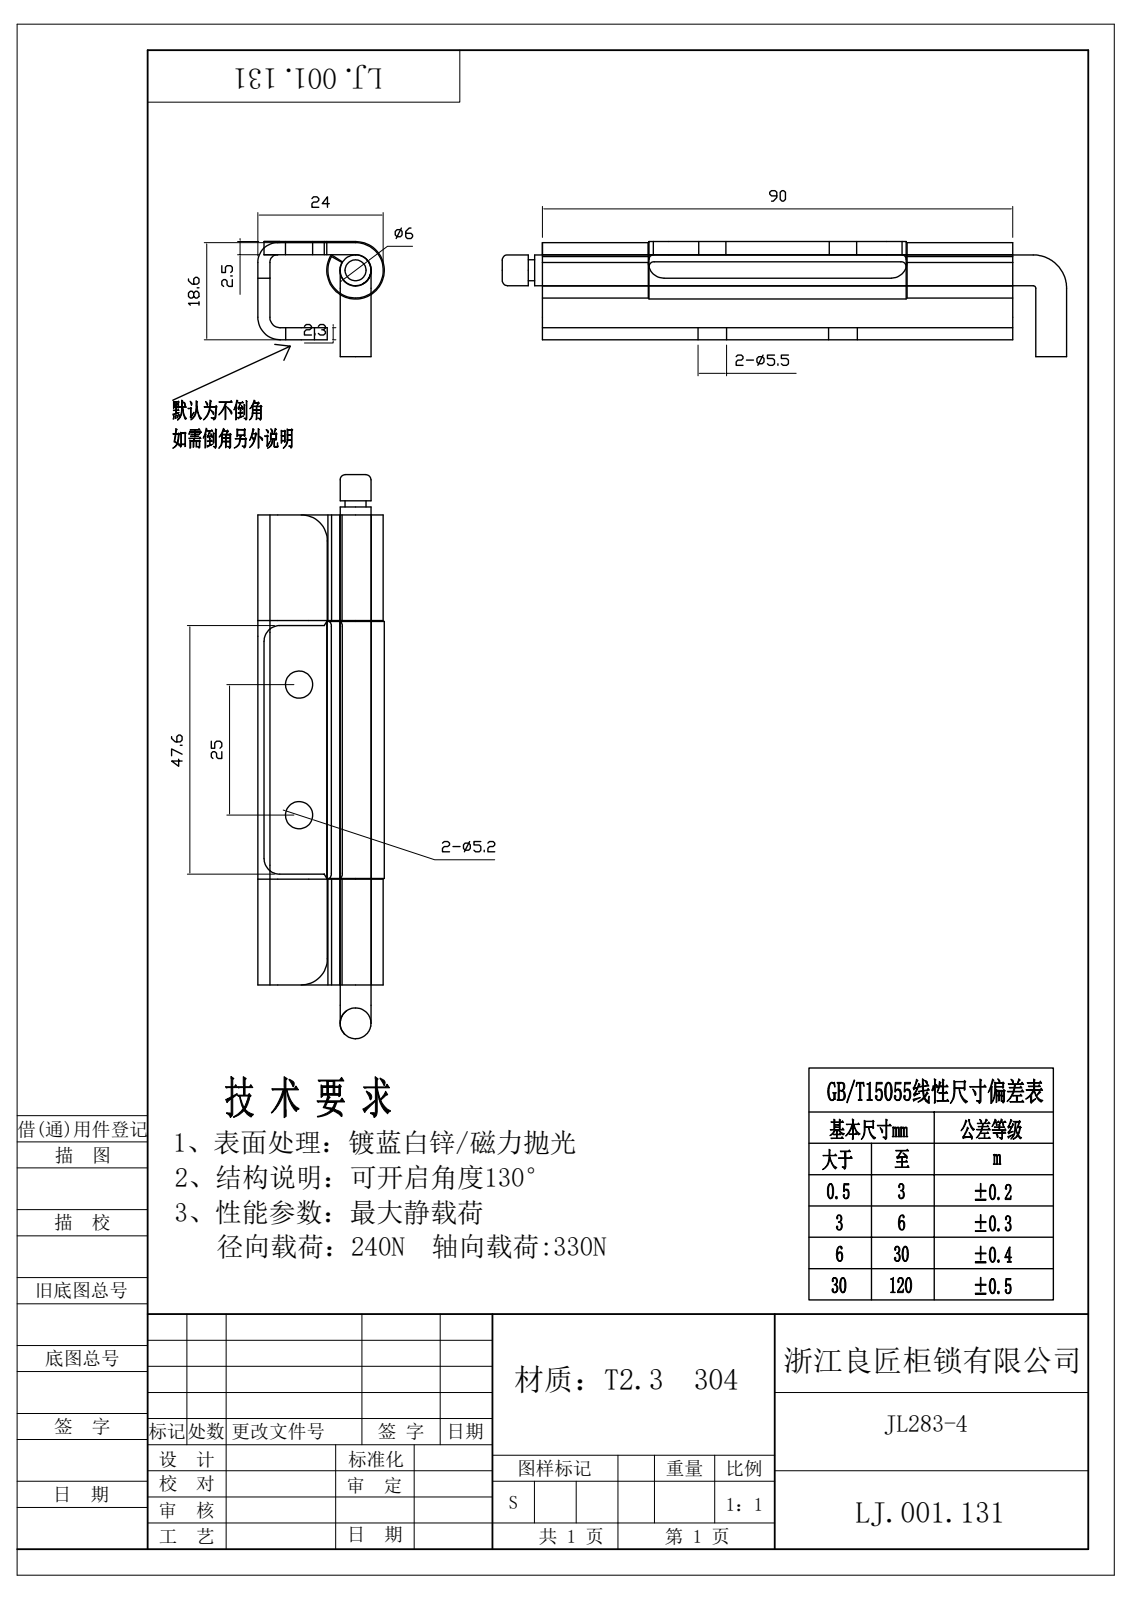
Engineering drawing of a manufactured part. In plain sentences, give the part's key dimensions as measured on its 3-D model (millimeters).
Its 3-D file was written by "Rhino 8.5 (CONFIG_CONTROL_DESIGN)". It is 6 solids with 152 faces: 60 planar, 80 cylindrical and 12 other. Overall it measures 108 by 83.1 by 22.05 millimeters. Its volume is 32 720 cubic millimeters and its surface area 28 774 square millimeters. Round holes: 4 of diameter 5.2, 4 of diameter 5.5, 2 of diameter 6. Round bosses or shafts: 4 of diameter 5.9, 2 of diameter 11, 2 of diameter 4. Partial cylindrical surfaces (rounded edges, fillets, slot ends): 4 of radius 2, 4 of radius 4.5, 4 of radius 5, 2 of radius 4.75, 2 of radius 7. The main face-to-face distances are 2.5, 16.5, 19, 14, 59.1, 61.6, 56.6, 21.25, 68.75, 13.3. The hole center spacings are 25, 25.01, 59.1, 0.6, 0.61, 58.5, 59.11, 59.71.
